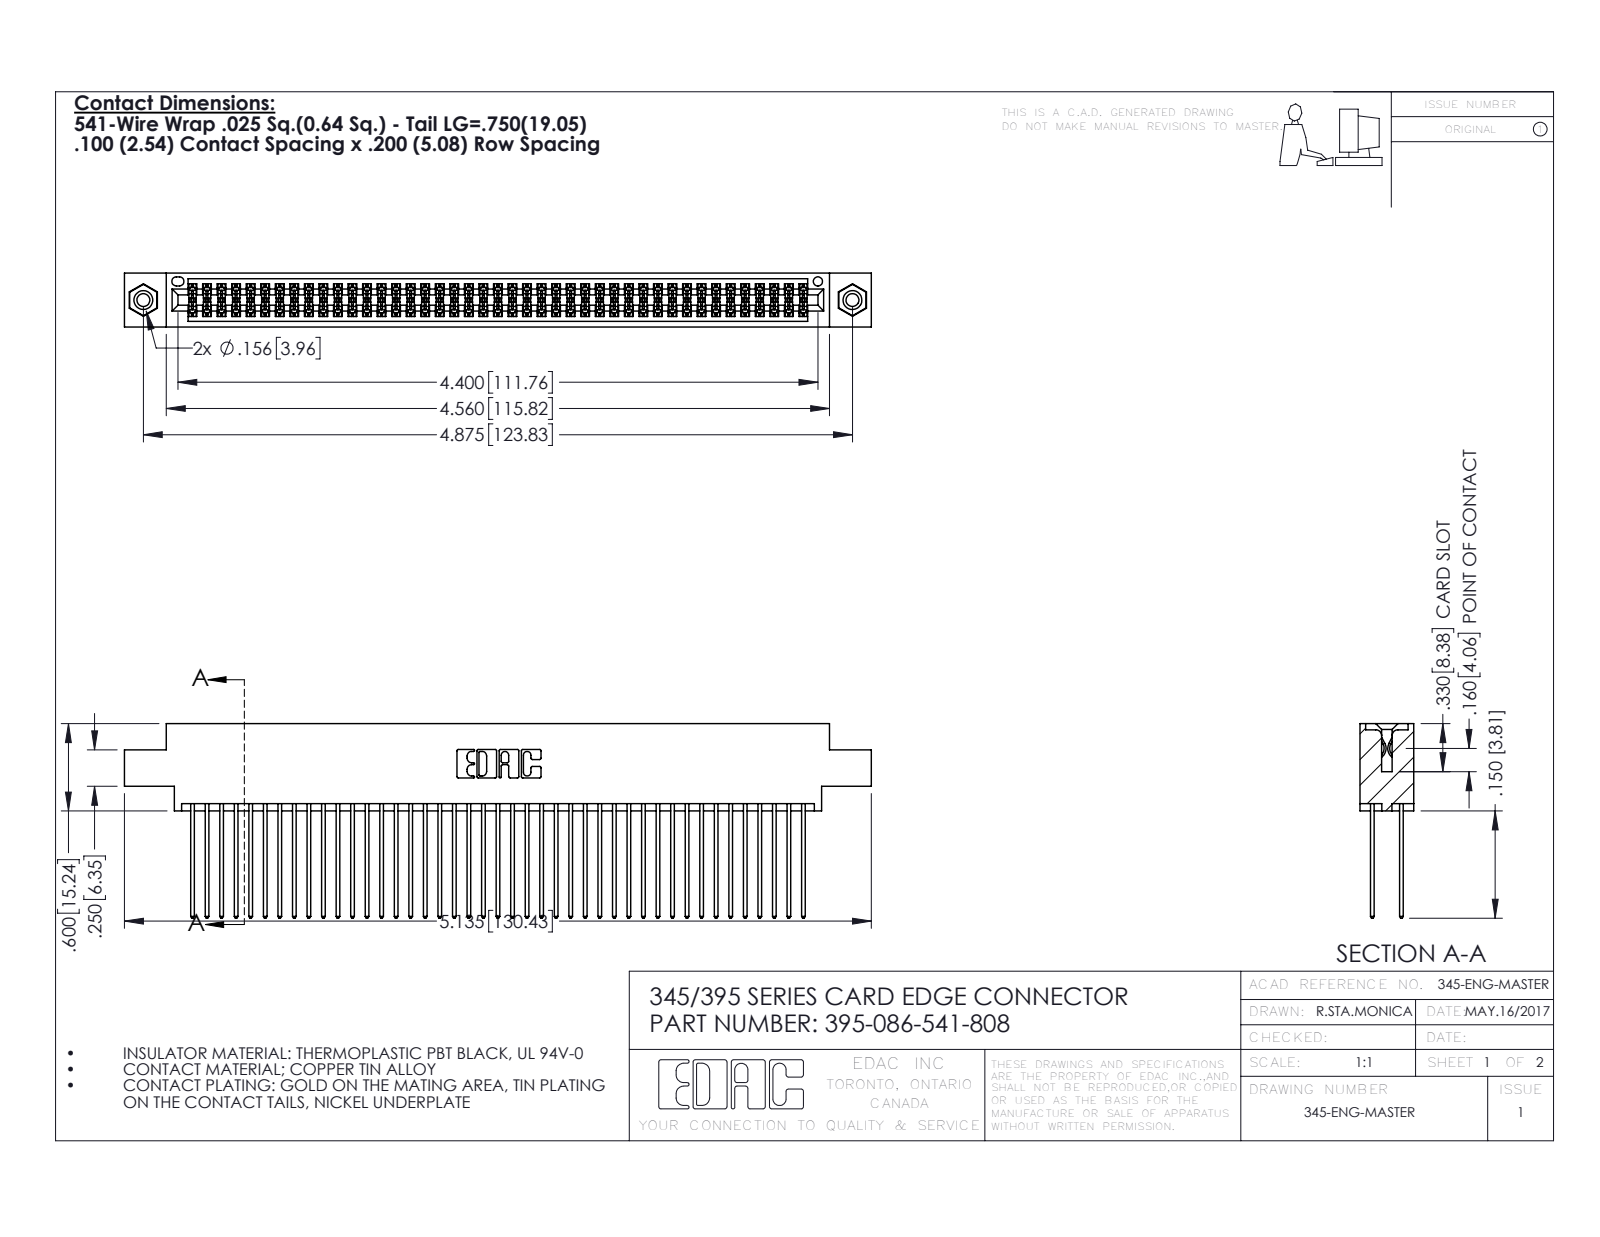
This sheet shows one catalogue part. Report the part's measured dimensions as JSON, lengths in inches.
{"part_name": "345-250-001_345-250-003-102; 345-292-001_345-293-141; 395-086-541-808; 345 Part_0.170 Offset - 0.156 Dia-TI", "step_written_by": "SolidWorks 2016 (CONFIG_CONTROL_DESIGN)", "units": "inches", "bodies": {"solids": 89, "faces": 4490, "planar": 2954, "cylindrical": 1520, "other": 16}, "overall_size": [5.135, 1.337, 0.37], "volume_in3": 0.797, "surface_area_in2": 33.77, "round_holes": [[0.089, 2], [0.125, 2], [0.156, 2], [0.064, 1]], "round_bosses_or_shafts": [[0.155, 2]], "partial_cylinders_radius": [[0.006, 129], [0.01, 86], [0.01, 22], [0.007, 6], [0.031, 6], [0.026, 3], [0.014, 2], [0.019, 2]], "face_to_face_distances": [0.072, 0.298, 0.2, 0.098, 0.272, 0.025, 0.37, 0.225, 0.175, 0.149], "hole_center_spacings": [0.27, 4.639, 4.875]}
